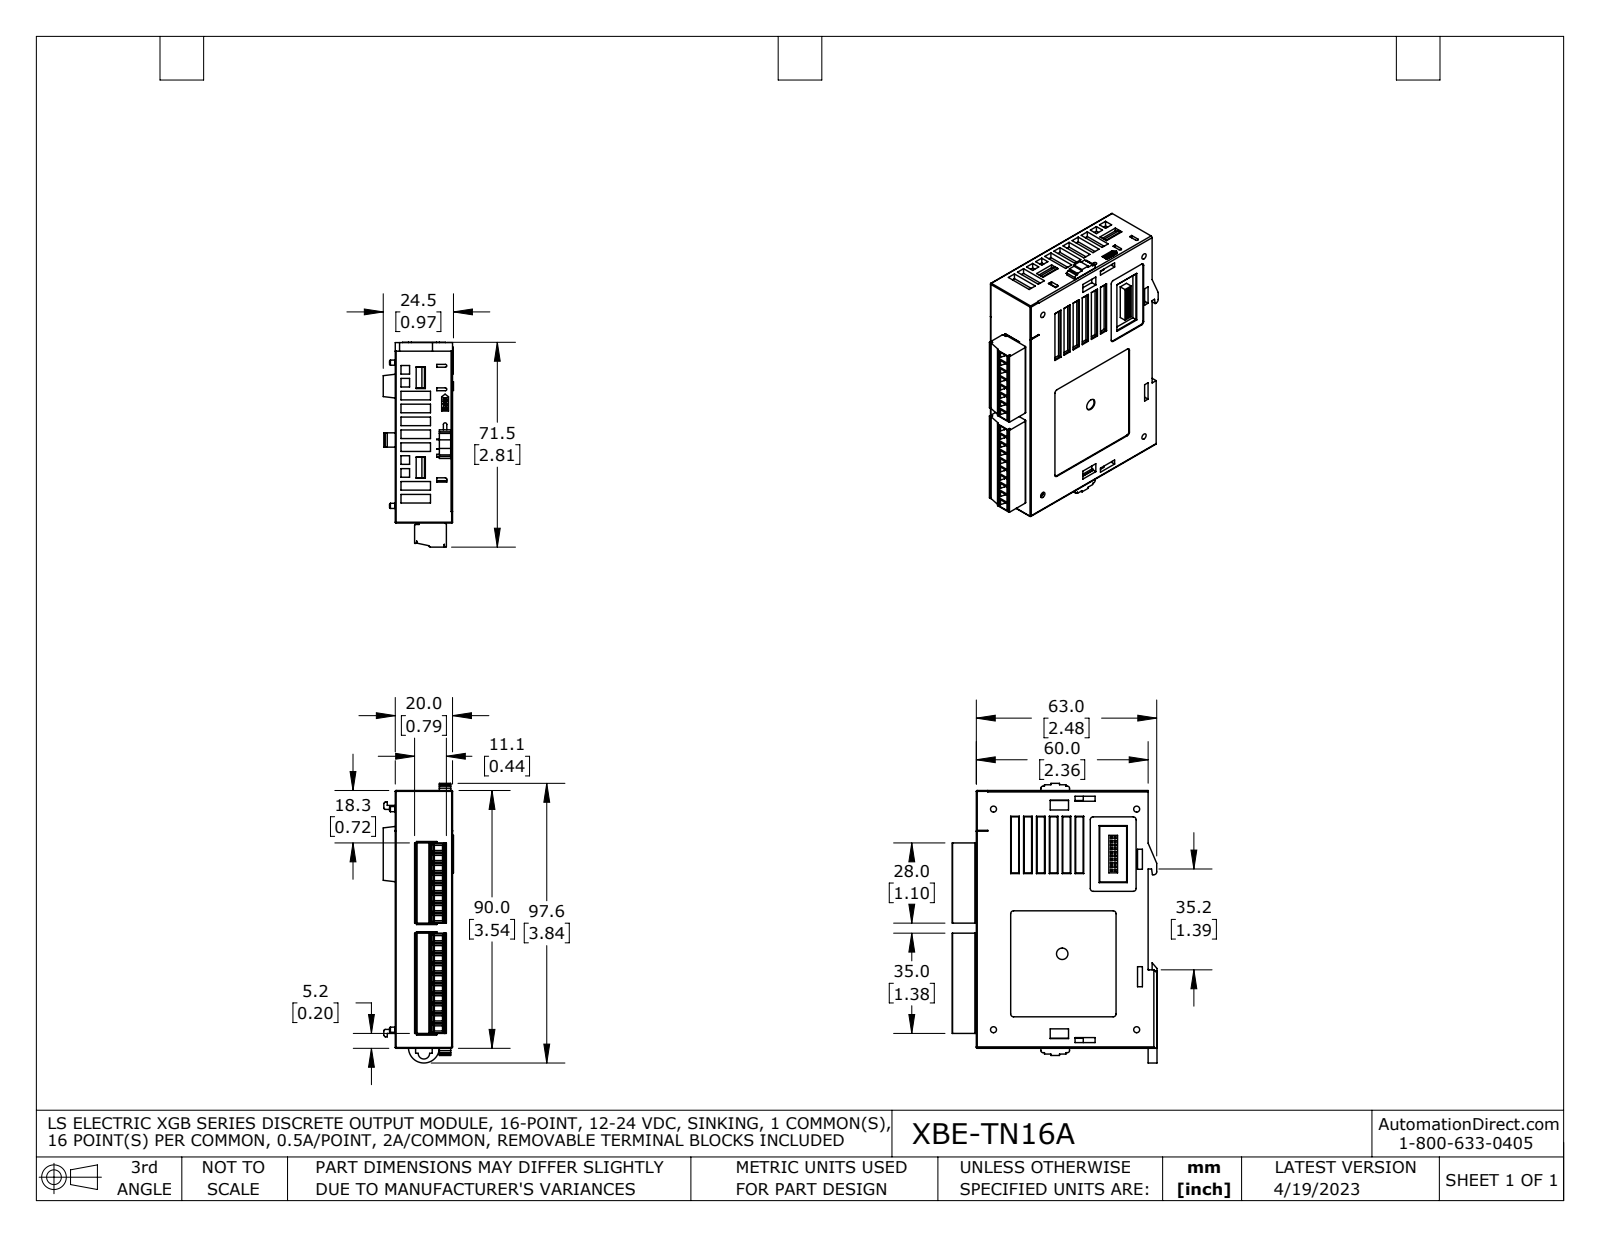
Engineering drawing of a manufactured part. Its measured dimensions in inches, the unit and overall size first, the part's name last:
Units: inches
Overall size (bounding box): 3.844 × 2.815 × 0.966
Round holes (diameter × count): ⌀0.108 ×18, ⌀0.116 ×18, ⌀0.083 ×4, ⌀0.071 ×2, ⌀0.157 ×1
Round bosses / shafts (diameter × count): ⌀0.11 ×18, ⌀0.071 ×6
Partial cylindrical surfaces — rounded edges, fillets, slot ends (radius × count): R0.008 ×74, R0.004 ×72, R0.012 ×54, R0.02 ×21, R0.062 ×18, R0.071 ×18, R0.039 ×11, R0.031 ×6
Main face-to-face distances: 0.787, 0.079, 0.039, 0.776, 0.709, 0.748, 2.362, 0.669, 0.067, 0.047
Hole centre spacings: 0.138, 0.276, 0.413, 0.551, 0.689, 0.827, 0.965, 1.102
Volume: 6.7 in³ · Surface area: 48.28 in²
Bodies: 1 solid, 2854 faces (2074 planar, 541 cylindrical, 239 other)
Part name (STEP PRODUCT): XBE-TP16A broken part cut1 coord fxt
STEP written by: SolidWorks 2021 (AUTOMOTIVE_DESIGN)
